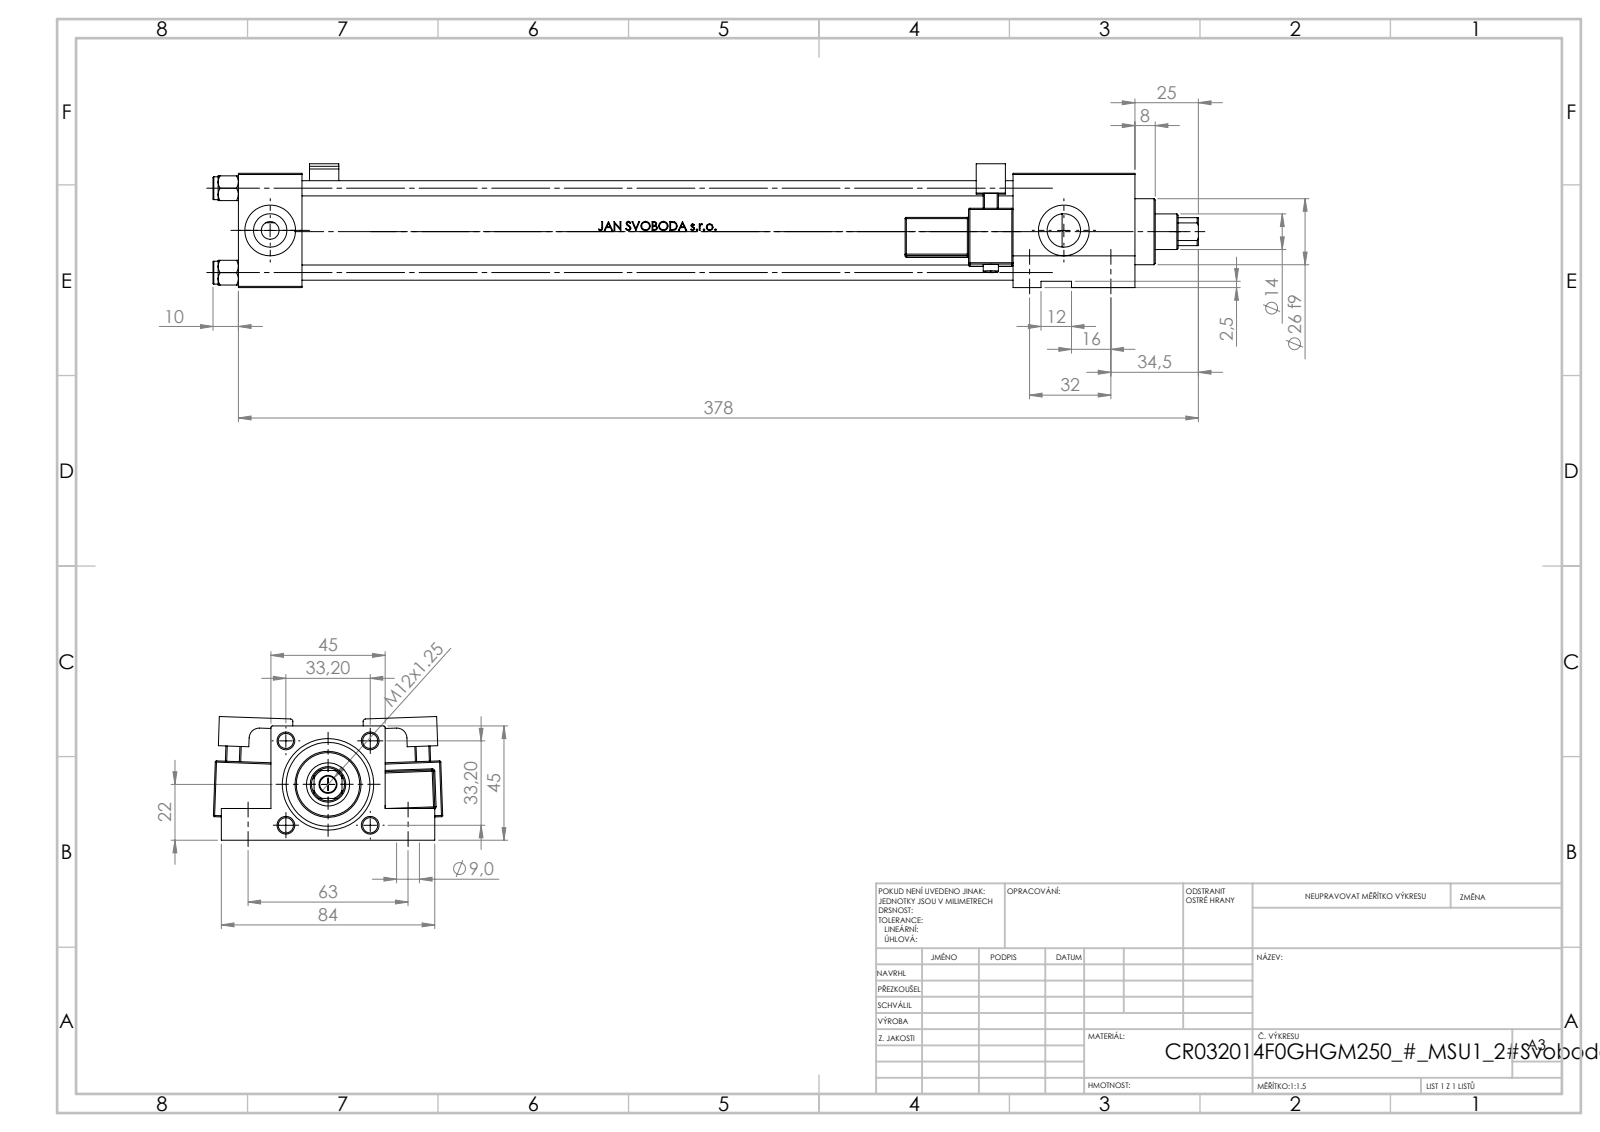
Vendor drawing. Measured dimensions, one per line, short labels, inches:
name: V215_VC_A; NUT_M5_F; V215CR_F_Body; V215CR_VCP_F (+2 more)
written by: SolidWorks 2019 (CONFIG_CONTROL_DESIGN)
unit: in
bodies: 13 solids, 1260 faces (498 planar, 186 cylindrical, 576 other)
size: 15.276 × 3.556 × 1.918
volume: 23.81 in³; area: 252.1 in²
holes: 4× ⌀0.236, 4× ⌀0.354, 2× ⌀0.276, 2× ⌀0.518, 2× ⌀0.787, 1× ⌀0.256, 1× ⌀0.551, 1× ⌀0.669, 1× ⌀0.945, 1× ⌀1.26, 1× ⌀1.299
bosses: 4× ⌀0.354, 2× ⌀0.236, 1× ⌀1.496, 1× ⌀1.024
rounds: 48× R0.02, 2× R0.039, 2× R0.098, 2× R0.157, 1× R0.256
face distances: 1.772, 0.984, 0.118, 11.024, 12.913, 12.008, 0.492, 1.673, 13.898, 1.89
hole spacings: 1.307, 0.911, 0.938, 1.26, 1.848, 2.48, 2.782, 12.303
